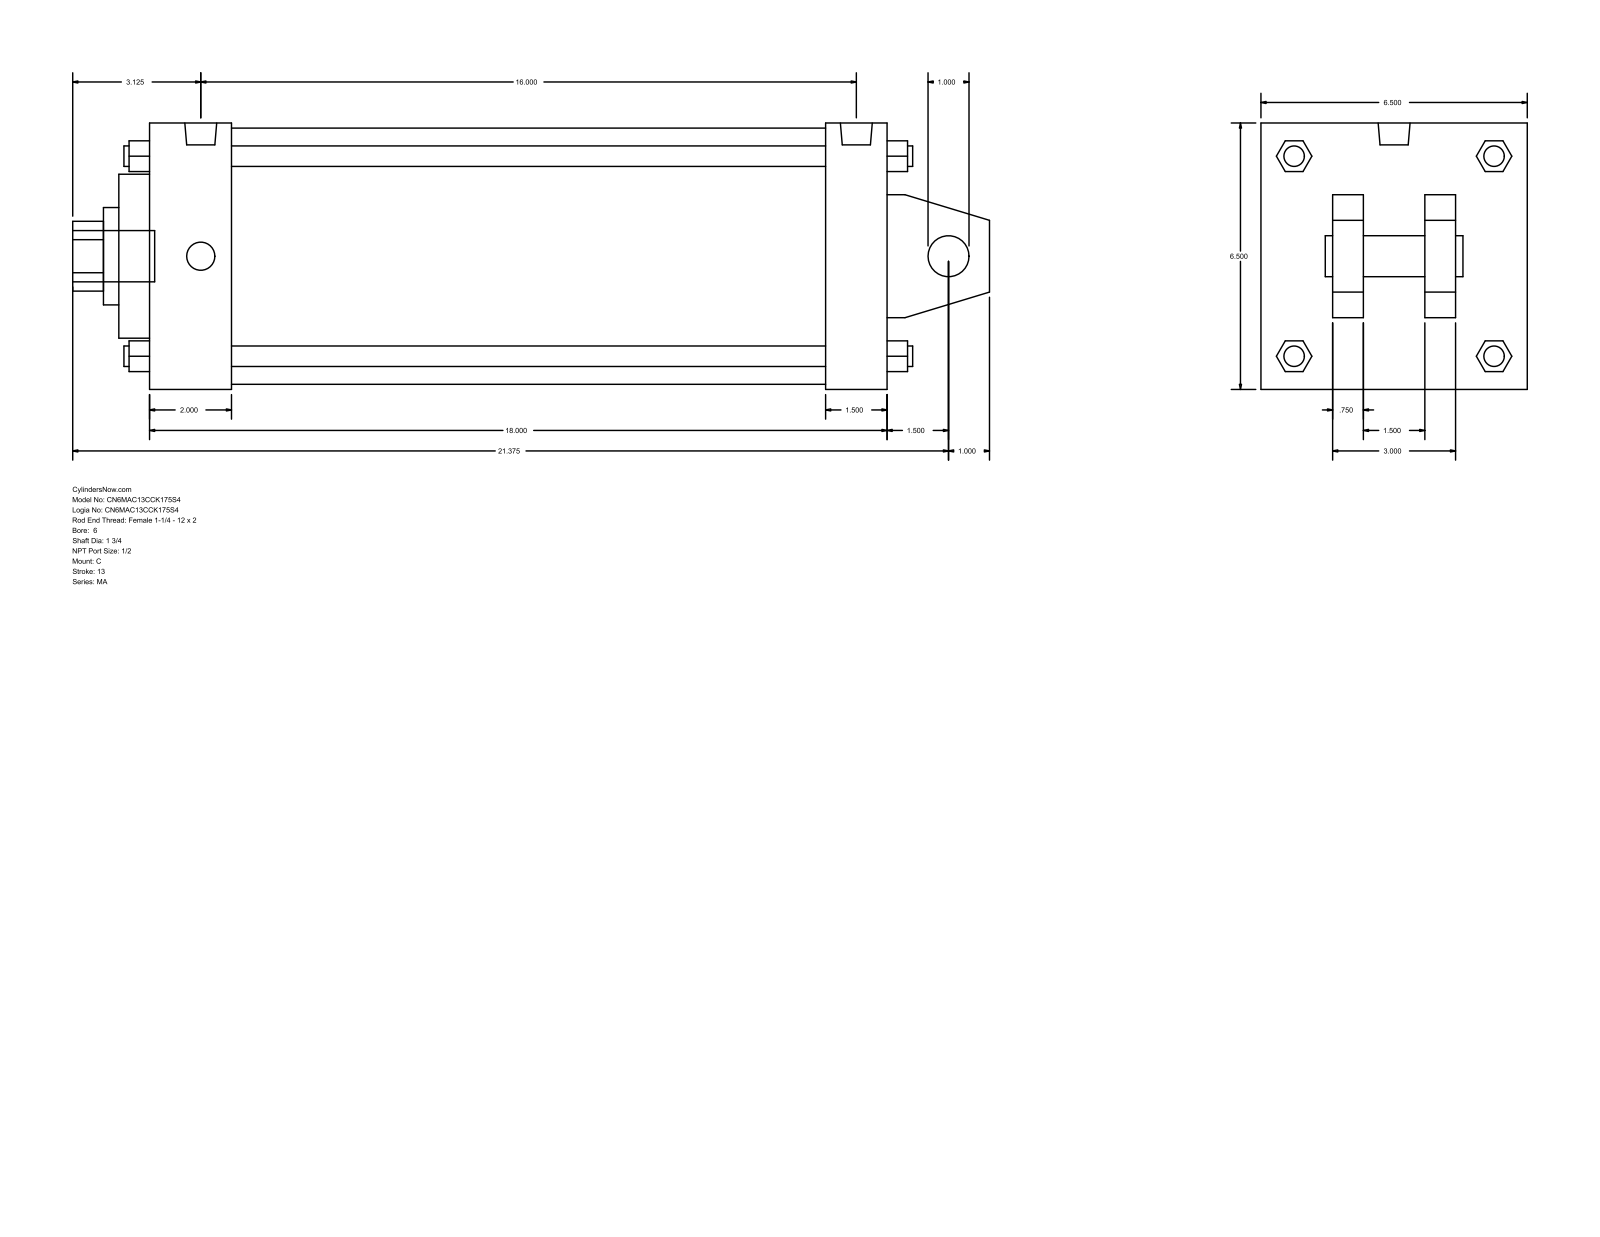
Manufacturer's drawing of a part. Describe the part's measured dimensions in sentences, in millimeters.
The part is named "MA_C__0600_1.75". Its 3-D file was written by "GSSL Pune (CONFIG_CONTROL_DESIGN)". It is 0 solids with 141 faces: 109 planar, 32 cylindrical and 0 other. Overall it measures 568.33 by 165.1 by 165.1 millimeters. Round holes: 1 of diameter 25.4, 1 of diameter 44.45, 1 of diameter 60.33, 1 of diameter 101.6, 1 of diameter 158.75. Round bosses or shafts: 4 of diameter 17.46, 4 of diameter 12.7, 2 of diameter 19.77, 1 of diameter 31.75. Partial cylindrical surfaces (rounded edges, fillets, slot ends): 1 of radius 21.63. The main face-to-face distances are 165.1, 457.2, 19.05, 101.6, 63.5, 44.45, 120.65, 57.15, 50.8, 406.4.
